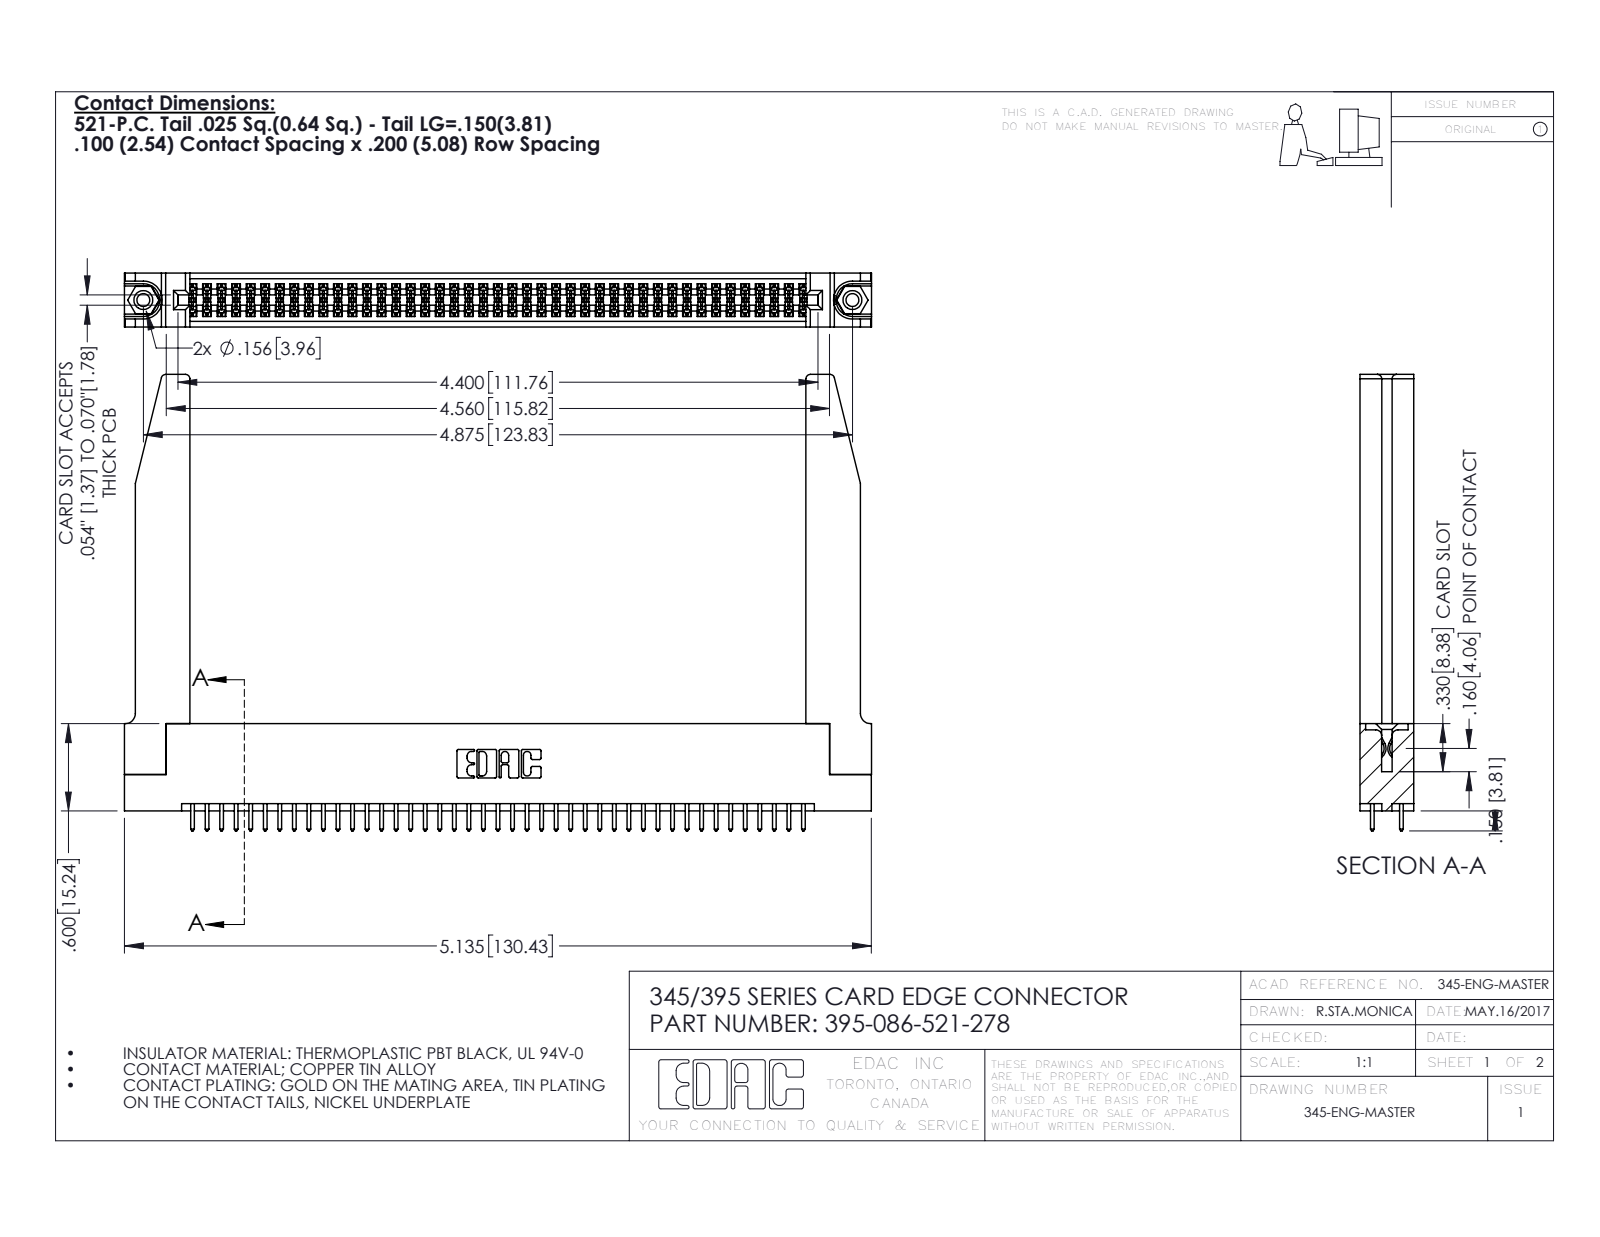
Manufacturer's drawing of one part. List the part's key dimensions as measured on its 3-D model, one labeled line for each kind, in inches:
Part name (STEP PRODUCT): 395-086-521-278; 345-220-078_345-220-078; 345-250-001_345-250-001-102; 345 Part_Flush Mounting Lugs - 0.156 Dia-TH (+1 more)
STEP written by: SolidWorks 2016 (CONFIG_CONTROL_DESIGN)
Units: inches
Bodies: 91 solids, 4660 faces (3060 planar, 1548 cylindrical, 52 other)
Overall size (bounding box): 5.136 × 3.137 × 0.37
Volume: 1.246 in³ · Surface area: 39.25 in²
Round holes (diameter × count): ⌀0.089 ×2, ⌀0.125 ×2, ⌀0.156 ×2, ⌀0.064 ×1
Round bosses / shafts (diameter × count): ⌀0.155 ×2
Partial cylindrical surfaces — rounded edges, fillets, slot ends (radius × count): R0.006 ×129, R0.01 ×86, R0.01 ×22, R0.03 ×8, R0.007 ×6, R0.031 ×6, R0.026 ×3, R0.014 ×2
Main face-to-face distances: 0.072, 0.37, 0.298, 0.2, 0.098, 0.272, 0.025, 0.225, 0.175, 0.148
Hole centre spacings: 0.27, 4.639, 4.875
